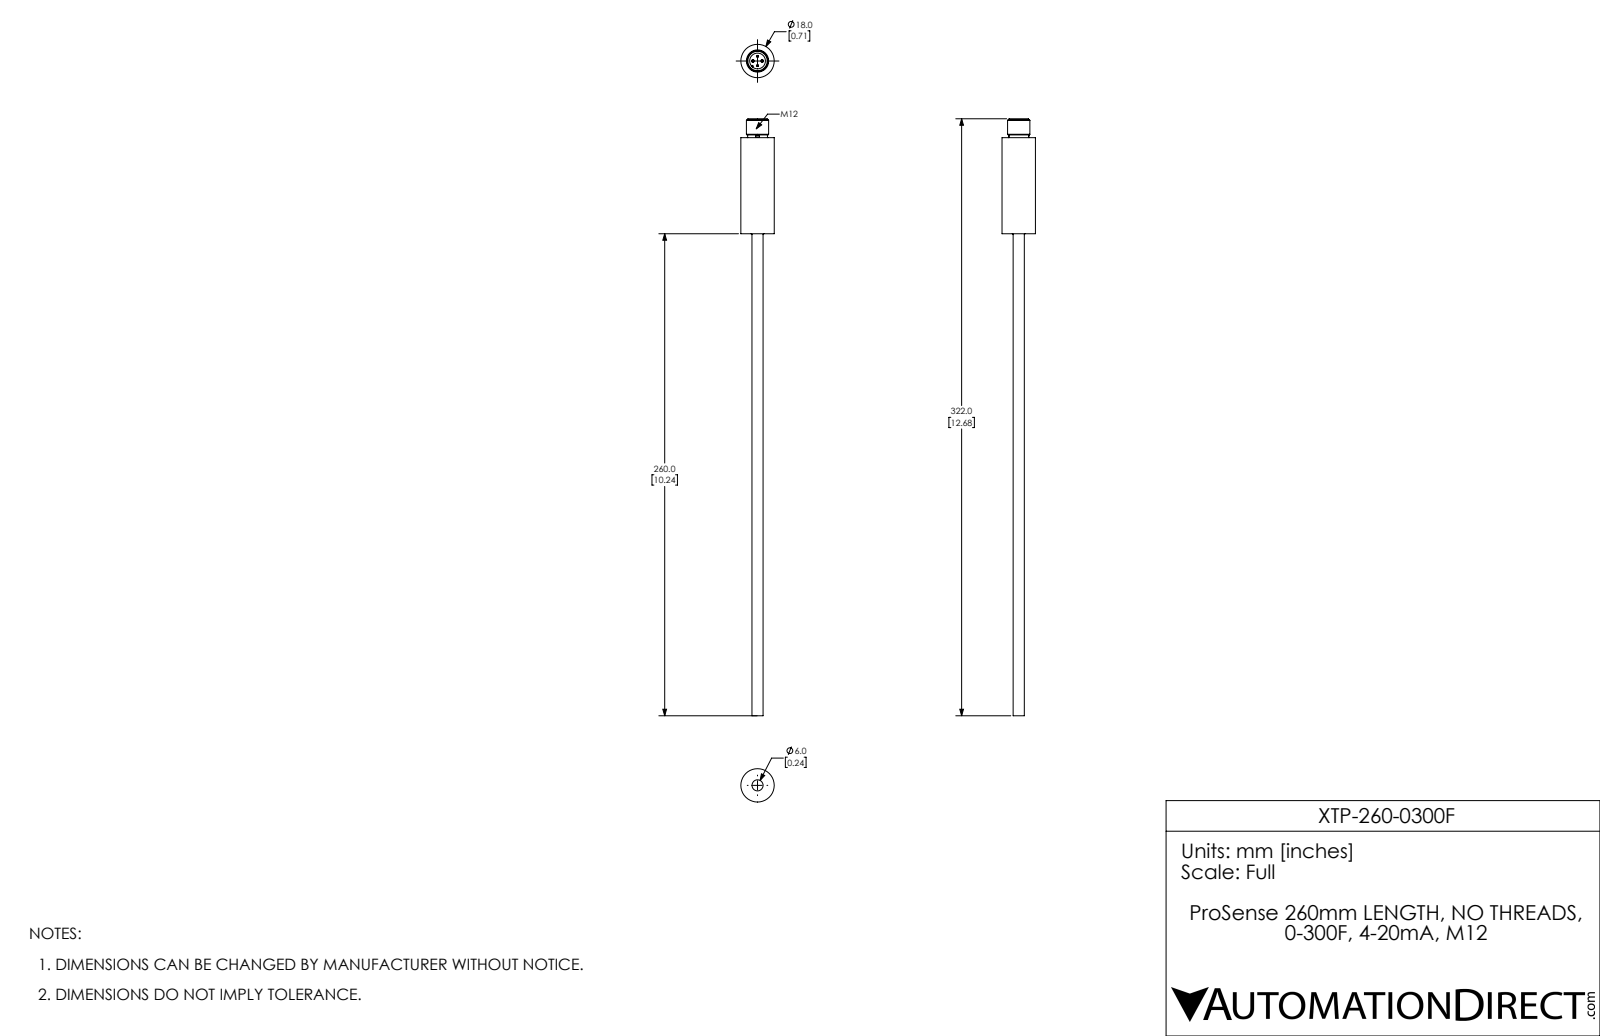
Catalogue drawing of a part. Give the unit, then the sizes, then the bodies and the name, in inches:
Units: inches
Overall size (bounding box): 12.677 × 0.709 × 0.709
Round holes (diameter × count): ⌀0.335 ×1
Round bosses / shafts (diameter × count): ⌀0.04 ×4, ⌀0.709 ×1, ⌀0.472 ×1, ⌀0.421 ×1, ⌀0.413 ×1, ⌀0.236 ×1
Partial cylindrical surfaces — rounded edges, fillets, slot ends (radius × count): R0.016 ×1
Main face-to-face distances: 2.039, 2.087, 0.047, 2.441, 0.402, 0.354, 10.236, 12.276, 12.323, 12.677
Volume: 1.29 in³ · Surface area: 14.01 in²
Bodies: 1 solid, 67 faces (24 planar, 21 cylindrical, 22 other)
Part name (STEP PRODUCT): XTP-260-0300F
STEP written by: SolidWorks 2017 (AUTOMOTIVE_DESIGN)
